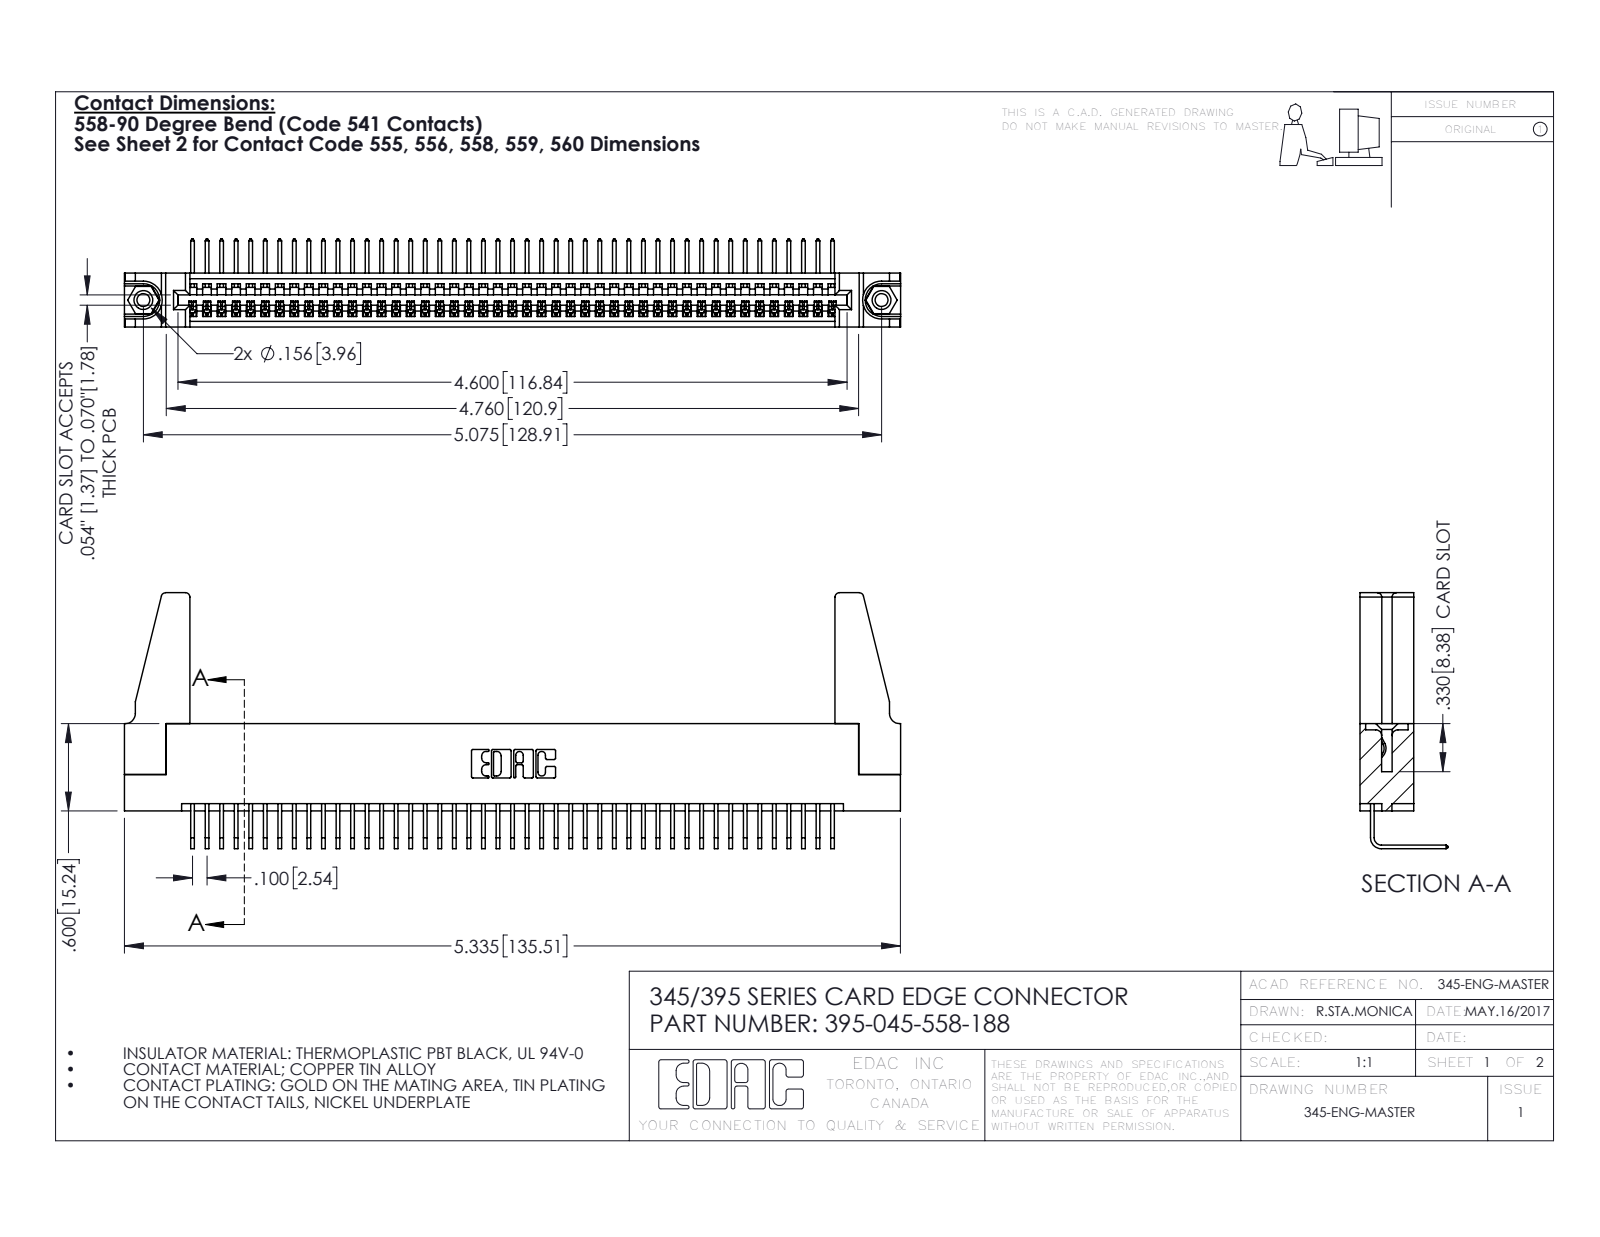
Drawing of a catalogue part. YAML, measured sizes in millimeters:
part_name: "345-250-001_345-250-001-102; 345 Part_Flush Mounting Lugs - 0.156 Dia-TH; 345-220-078_345-220-088; 345-292-001_558 Tail - 2 (+1 more)"
step_written_by: "SolidWorks 2016 (CONFIG_CONTROL_DESIGN)"
units: millimeters
bodies: {solids: 50, faces: 2950, planar: 2042, cylindrical: 892, other: 16}
overall_size: [135.5, 44.7, 15.4]
volume: 16300
surface_area: 21390
round_holes:
  - {diameter: 2.3, count: 2}
  - {diameter: 3.2, count: 2}
  - {diameter: 4, count: 2}
  - {diameter: 1.6, count: 1}
round_bosses_or_shafts:
  - {diameter: 3.9, count: 2}
partial_cylinders:
  - {radius: 0.2, count: 90}
  - {radius: 0.3, count: 22}
  - {radius: 0.8, count: 8}
  - {radius: 0.2, count: 6}
  - {radius: 0.8, count: 6}
  - {radius: 0.7, count: 3}
  - {radius: 0.8, count: 2}
  - {radius: 1, count: 2}
face_to_face_distances: [1.8, 7.6, 9.4, 5.1, 2.5, 6.9, 0.6, 5.7, 3.8, 1.8]
hole_center_spacings: [6.9, 122.9, 128.9]
